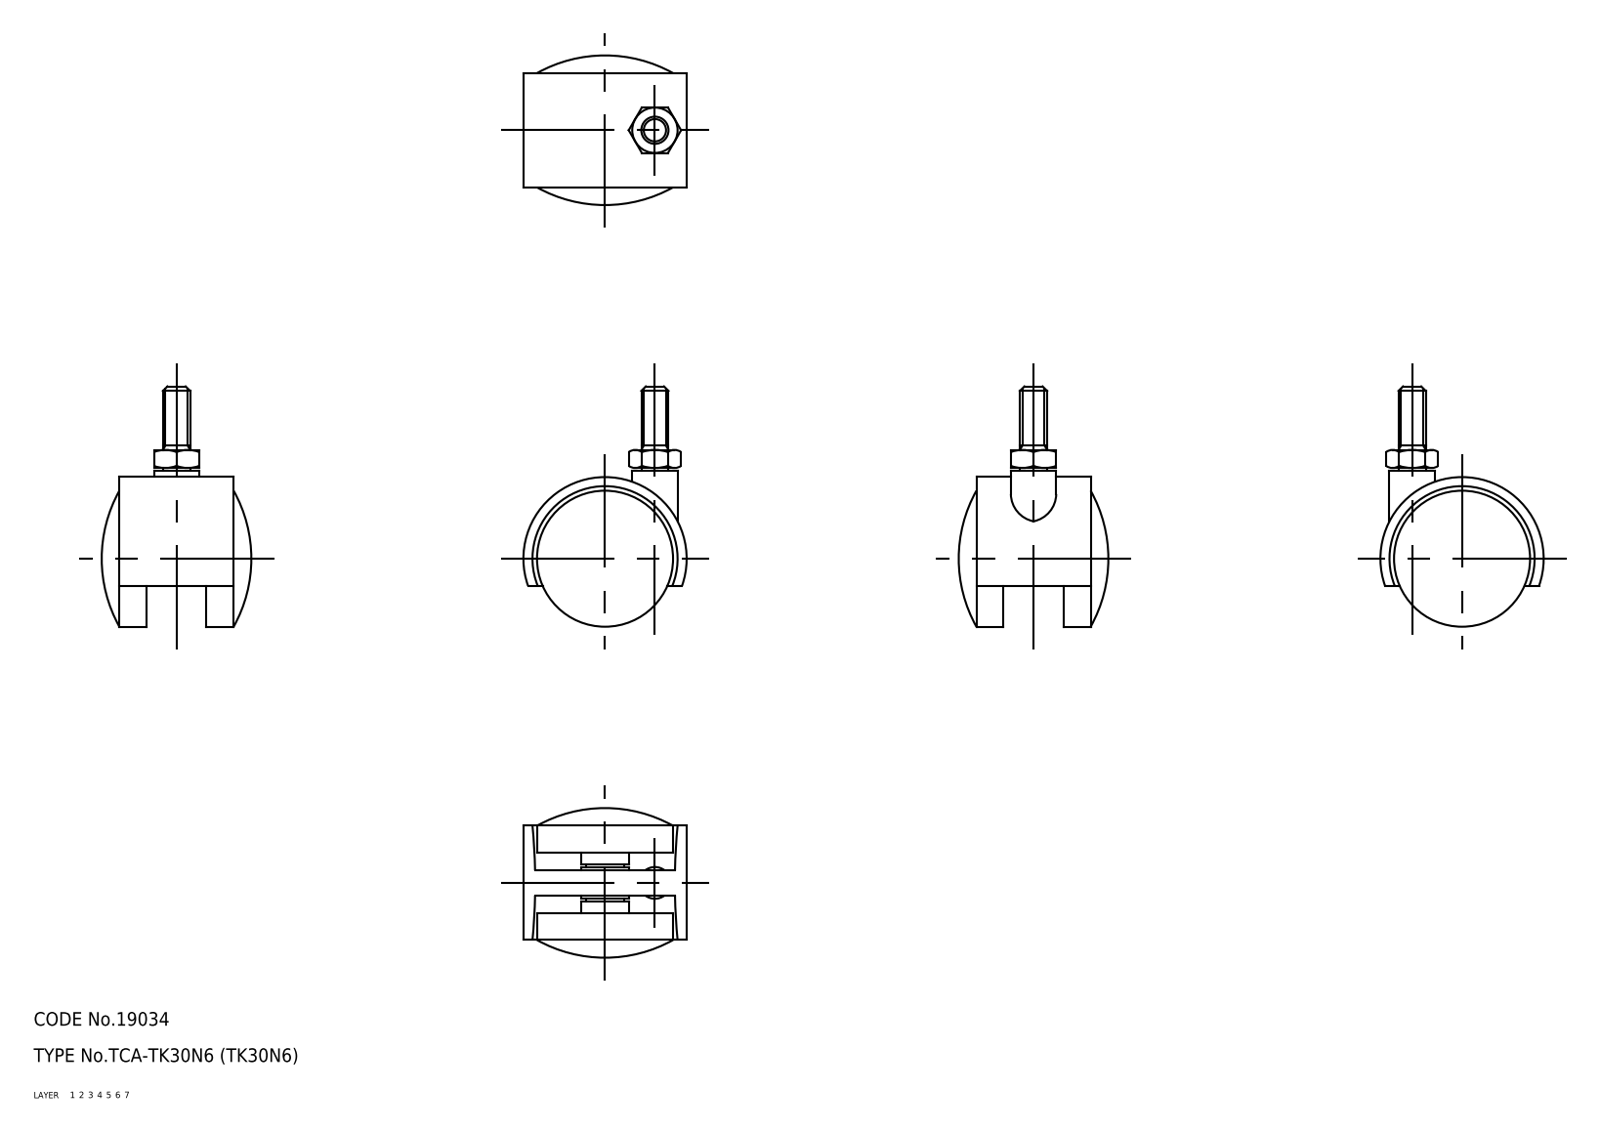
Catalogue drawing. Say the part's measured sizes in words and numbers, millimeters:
The part is named "wheel; main shaft; TK30N6_3811_36". Its 3-D file was written by "CADfix (AUTOMOTIVE_DESIGN)". It is 4 solids with 112 faces: 0 planar, 0 cylindrical and 112 other. Overall it measures 53 by 36 by 33 millimeters. Its volume is 15 909 cubic millimeters and its surface area 11 721 square millimeters.
